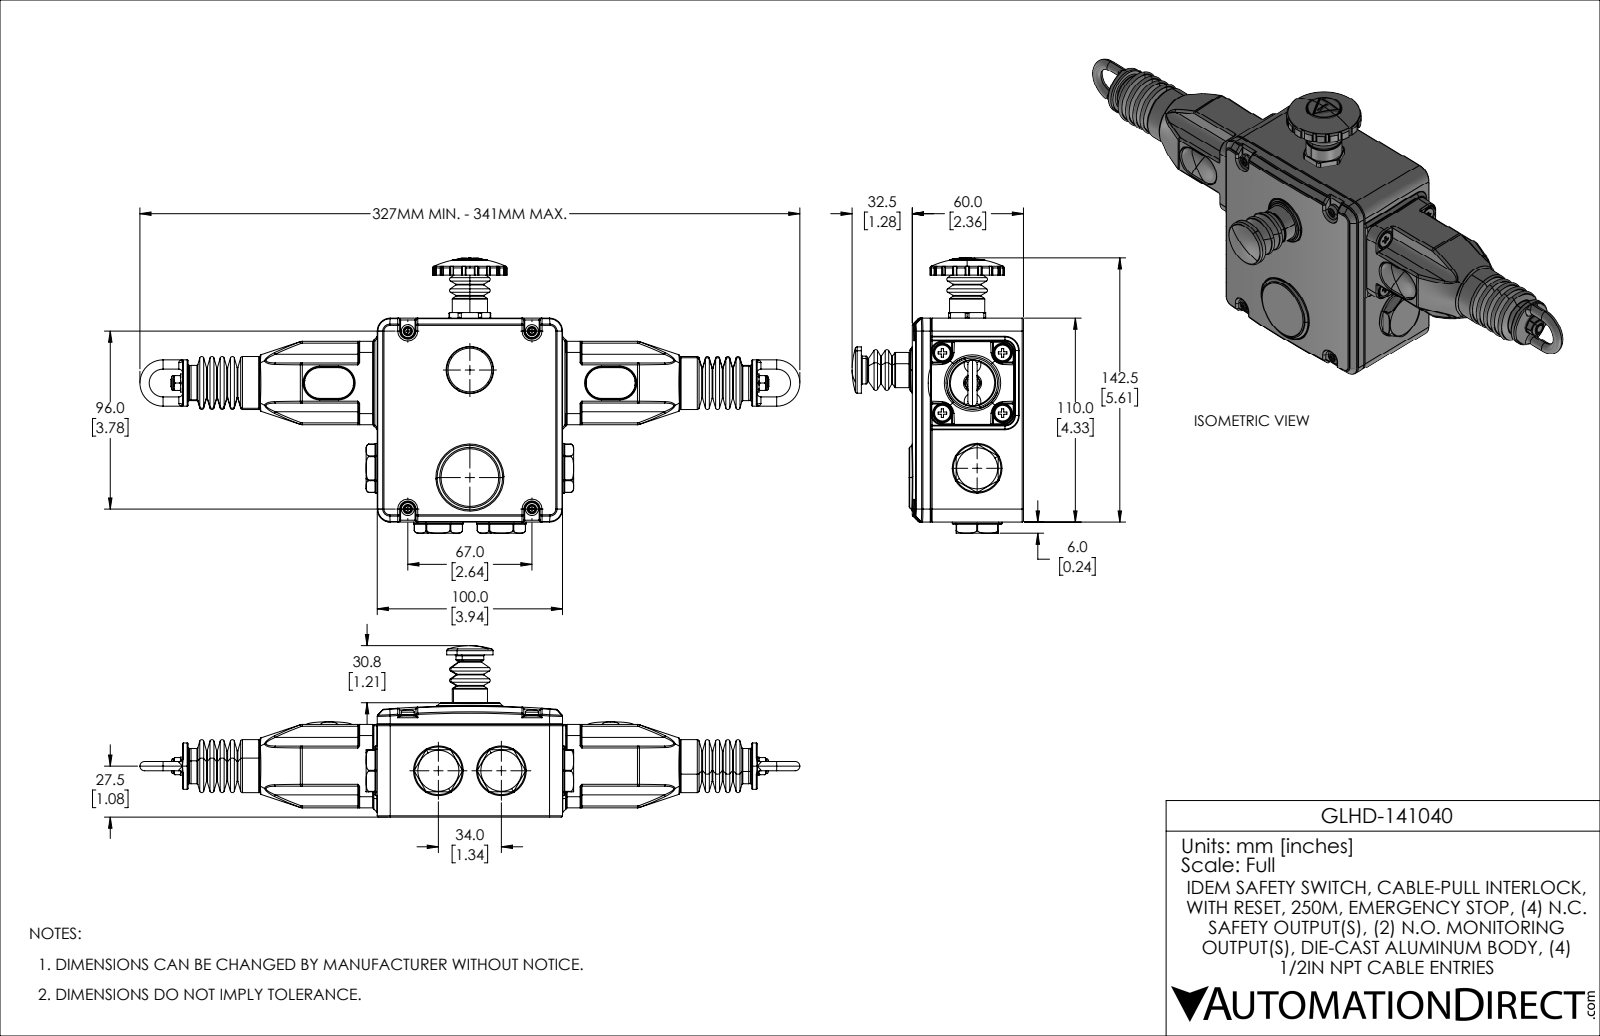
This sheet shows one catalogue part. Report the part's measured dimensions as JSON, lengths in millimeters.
{"part_name": "GLHD-141040", "step_written_by": "SolidWorks 2021 (AUTOMOTIVE_DESIGN)", "units": "millimeters", "bodies": {"solids": 39, "faces": 4817, "planar": 1101, "cylindrical": 1659, "other": 2057}, "overall_size": [356.2, 148.5, 92.5], "volume_mm3": 344800, "surface_area_mm2": 215200, "round_holes": [[5, 11], [9, 6], [5.3, 5], [2.4, 4], [3.3, 4], [4, 4], [4.8, 4], [5.4, 4], [5.8, 4], [9.5, 4], [3, 3], [4.4, 3]], "round_bosses_or_shafts": [[6, 7], [7, 5], [8.5, 4], [4.4, 4], [3.5, 4], [1.3, 4], [26.8, 3], [19.4, 3]], "partial_cylinders_radius": [[0.5, 272], [1, 138], [0.2, 136], [0.7, 80], [0.3, 26], [0.1, 15], [0.2, 14], [2, 14]], "face_to_face_distances": [54.8, 3.5, 2.9, 51.9, 45, 110, 11.7, 98.5, 4, 1.4], "hole_center_spacings": [9.5, 23, 32.5, 48, 48.6, 76.5, 88.6, 96]}
